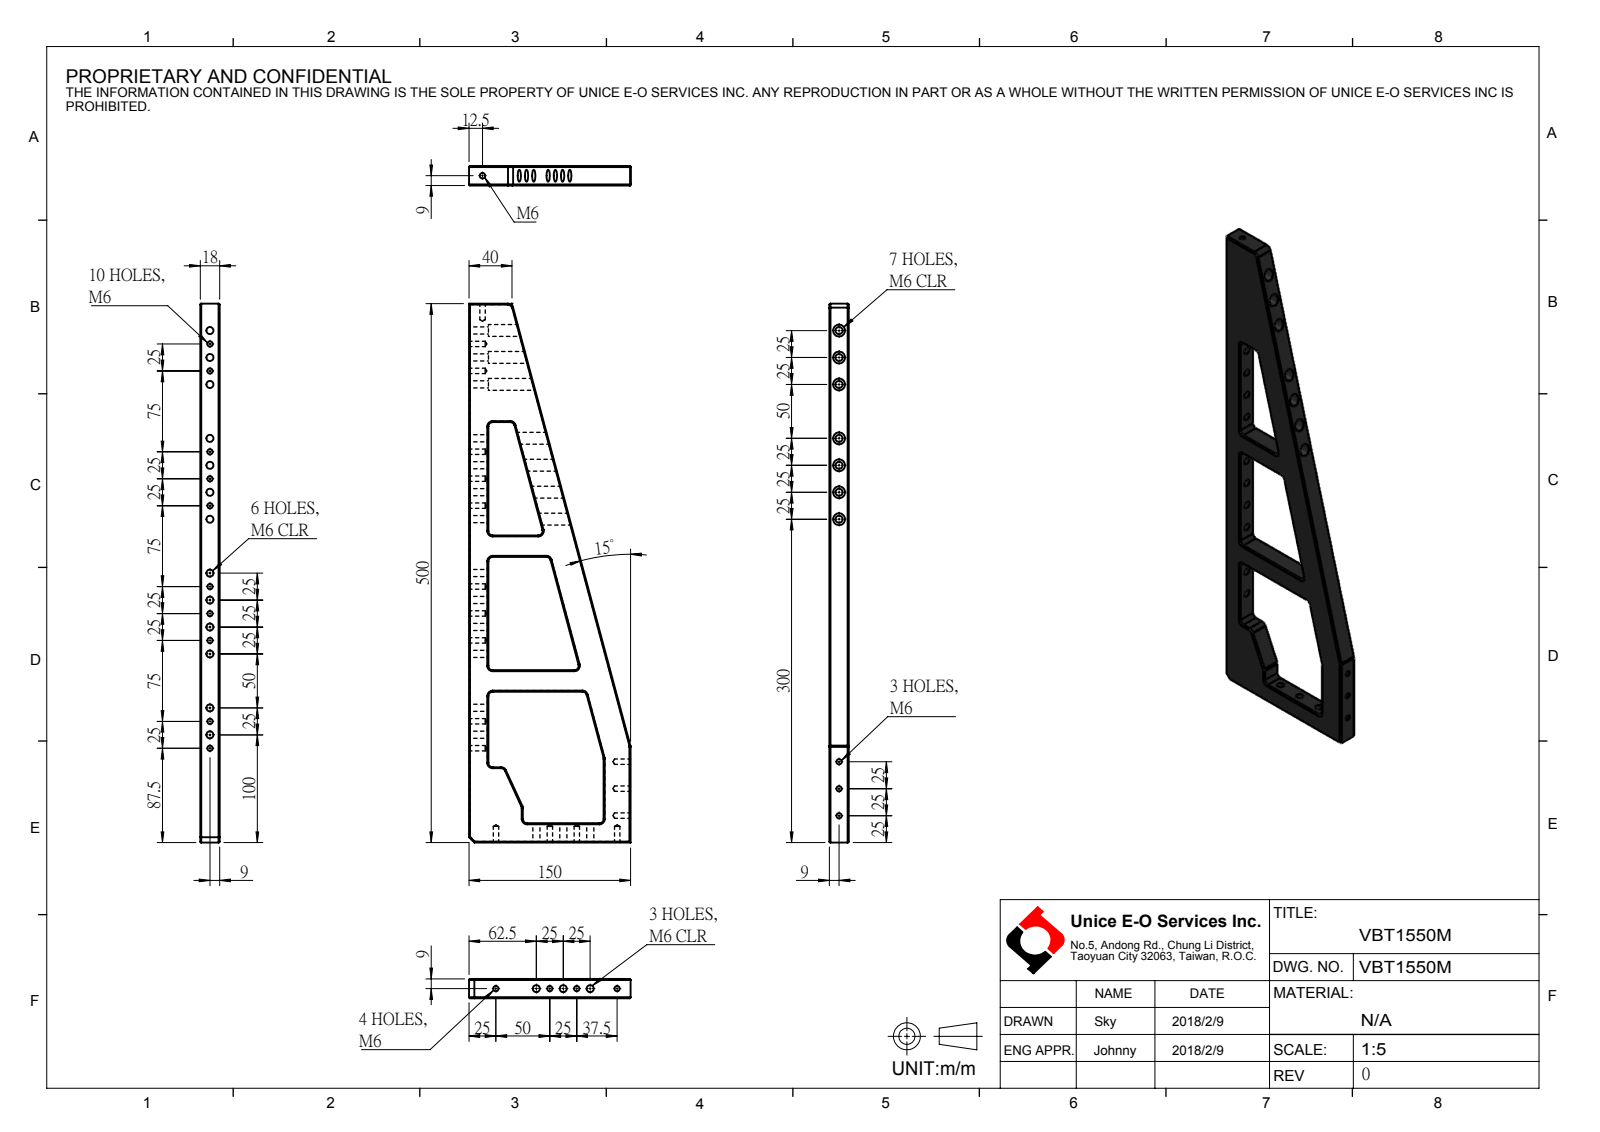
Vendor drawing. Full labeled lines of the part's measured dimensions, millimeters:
Part name (STEP PRODUCT): U-F1-VBT1550M1-D0; VBT1550M
STEP written by: SolidWorks 2016 (AUTOMOTIVE_DESIGN)
Units: millimetres
Bodies: 1 solid, 245 faces (27 planar, 146 cylindrical, 72 other)
Overall size (bounding box): 500 × 150 × 18
Volume: 500 683 mm³ · Surface area: 114 277 mm²
Round holes (diameter × count): ⌀5 ×18, ⌀6.6 ×16, ⌀11 ×7
Partial cylindrical surfaces — rounded edges, fillets, slot ends (radius × count): R1 ×38, R4 ×14, R5 ×4
Main face-to-face distances: 18, 125, 20, 27.17, 132, 150, 140, 27.15, 160, 105
Hole centre spacings: 12.5, 25, 125, 37.5, 50, 100, 112.5, 75
